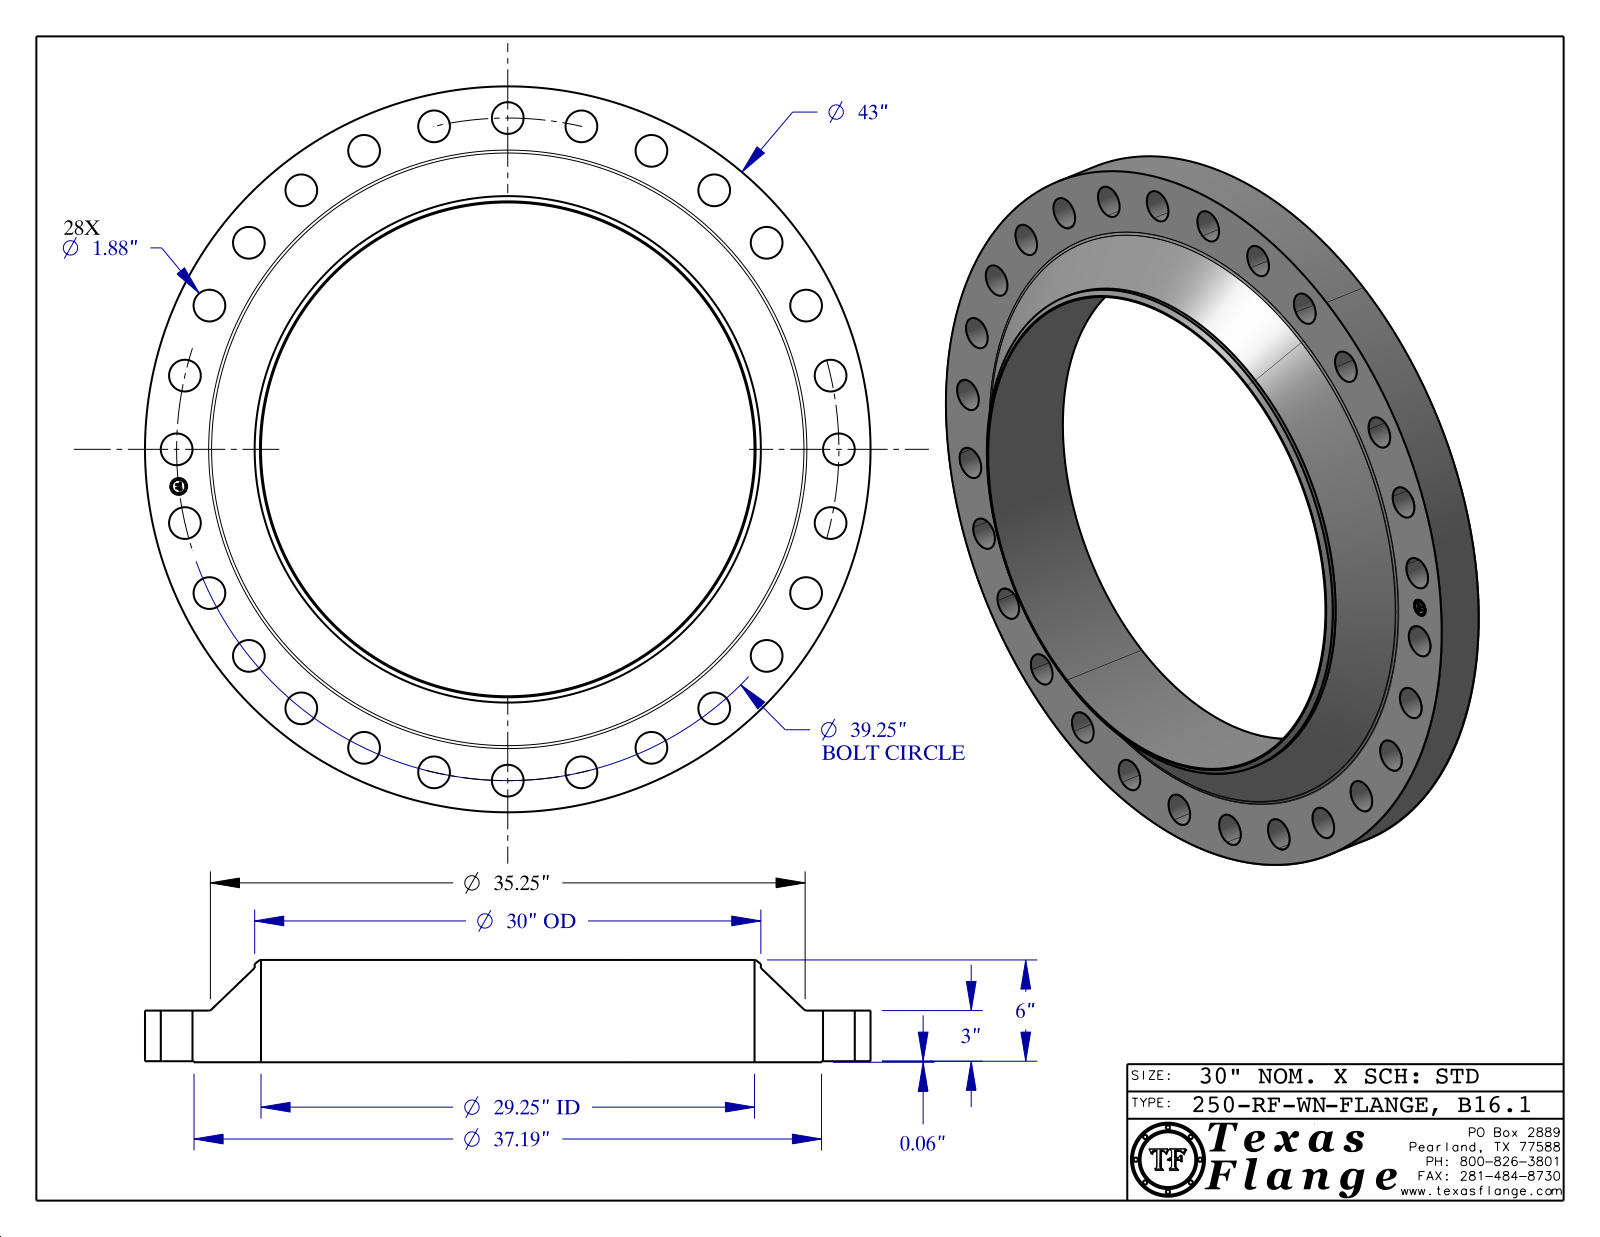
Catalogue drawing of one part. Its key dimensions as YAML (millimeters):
part_name: "250-RF-WN, B16.1"
step_written_by: "CATIA V5 STEP AP203 (CONFIG_CONTROL_DESIGN)"
units: millimeters
bodies: {solids: 1, faces: 459, planar: 369, cylindrical: 84, other: 6}
overall_size: [1092.2, 1092.2, 153.99]
volume: 42040000
surface_area: 1938000
round_holes:
  - {diameter: 47.75, count: 28}
  - {diameter: 25.4, count: 1}
  - {diameter: 742.95, count: 1}
round_bosses_or_shafts:
  - {diameter: 1.54, count: 8}
  - {diameter: 1092.2, count: 1}
  - {diameter: 944.63, count: 1}
  - {diameter: 762, count: 1}
  - {diameter: 20.01, count: 1}
face_to_face_distances: [77.79, 76.2, 1.59, 153.99, 152.4, 77.41, 75.82, 0.38, 76.58, 7.58]
hole_center_spacings: [111.62, 221.84, 329.27, 432.56, 530.41, 898.22, 621.59, 844.14]
